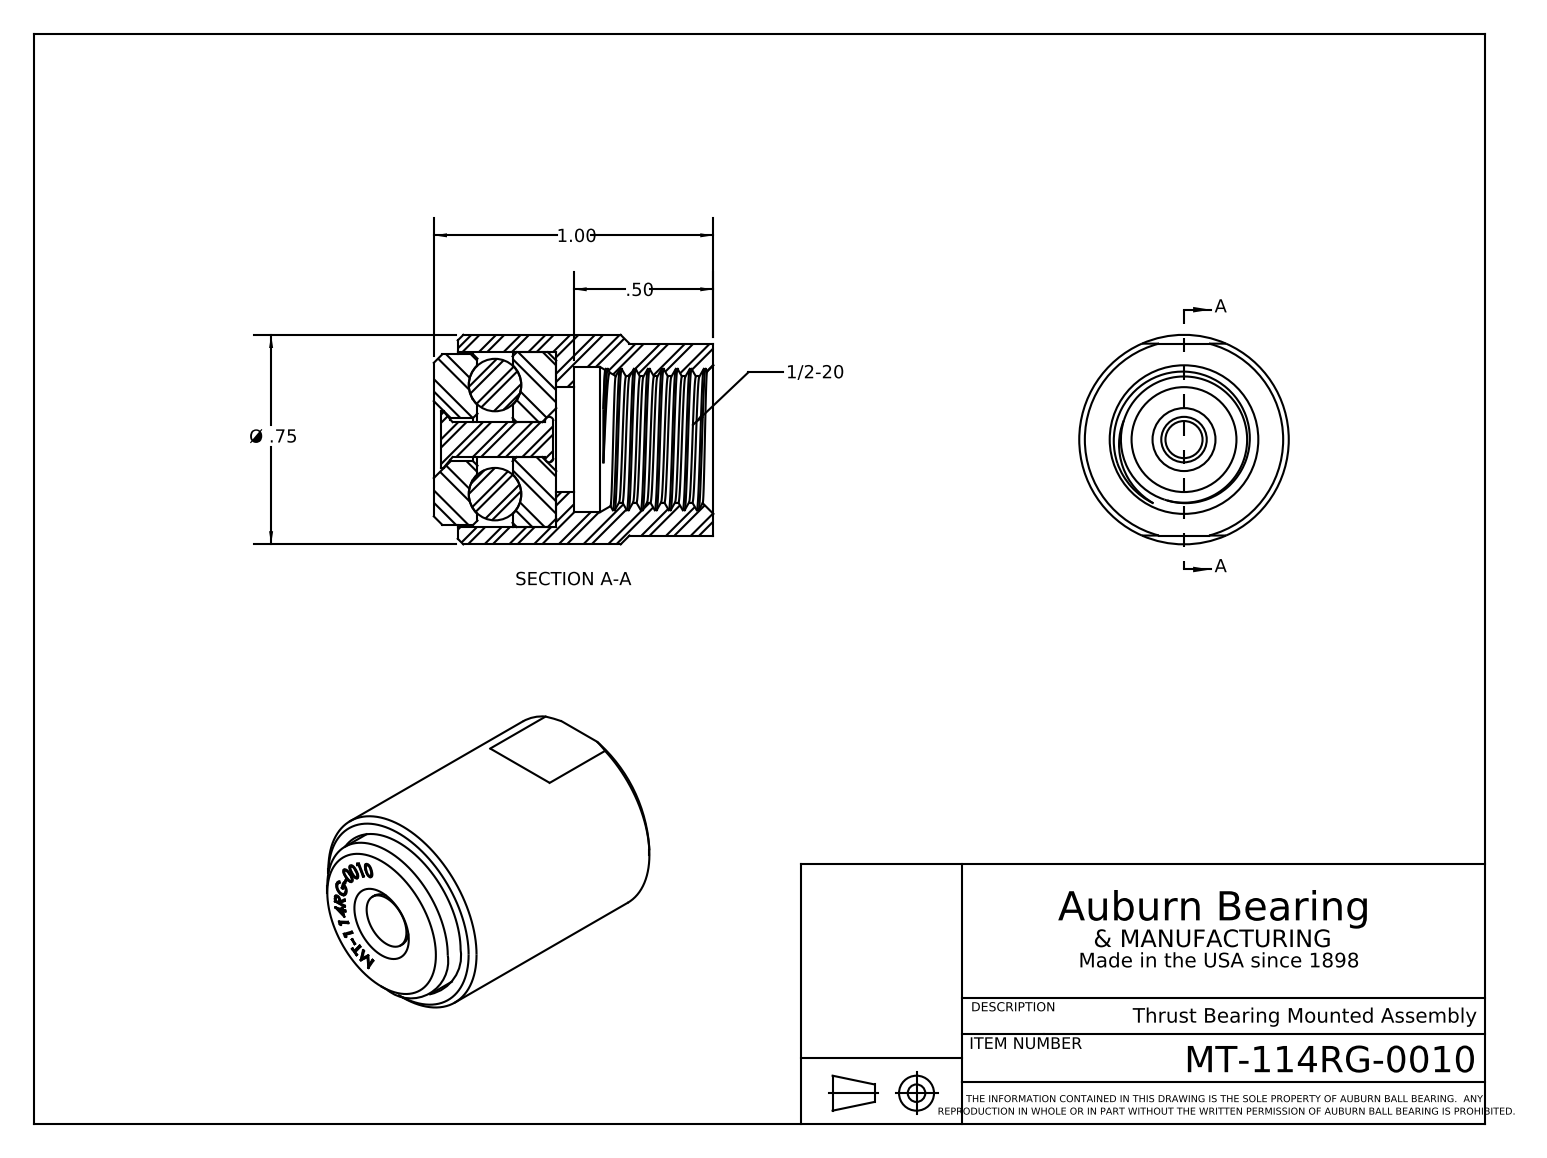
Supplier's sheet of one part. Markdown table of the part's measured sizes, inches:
| quantity | value |
| --- | --- |
| part name | MT-114RG-0010 |
| STEP written by | SolidWorks 2020 (CONFIG_CONTROL_DESIGN) |
| units | inches |
| bodies | 10 solids, 239 faces (111 planar, 36 cylindrical, 92 other) |
| overall size | 0.999 × 0.749 × 0.749 |
| volume | 0.293 in³ |
| surface area | 7.302 in² |
| round holes (diameter × count) | 0.125 × 1, 0.156 × 1, 0.375 × 1, 0.451 × 1, 0.52 × 1, 0.624 × 1, 0.628 × 1 |
| round bosses / shafts (diameter × count) | 0.749 × 1, 0.625 × 1, 0.609 × 1, 0.201 × 1 |
| main face-to-face distances | 0.438, 1, 0.562, 0.156, 0.281, 0.5, 0.062, 0.5, 0.686, 0.218 |
